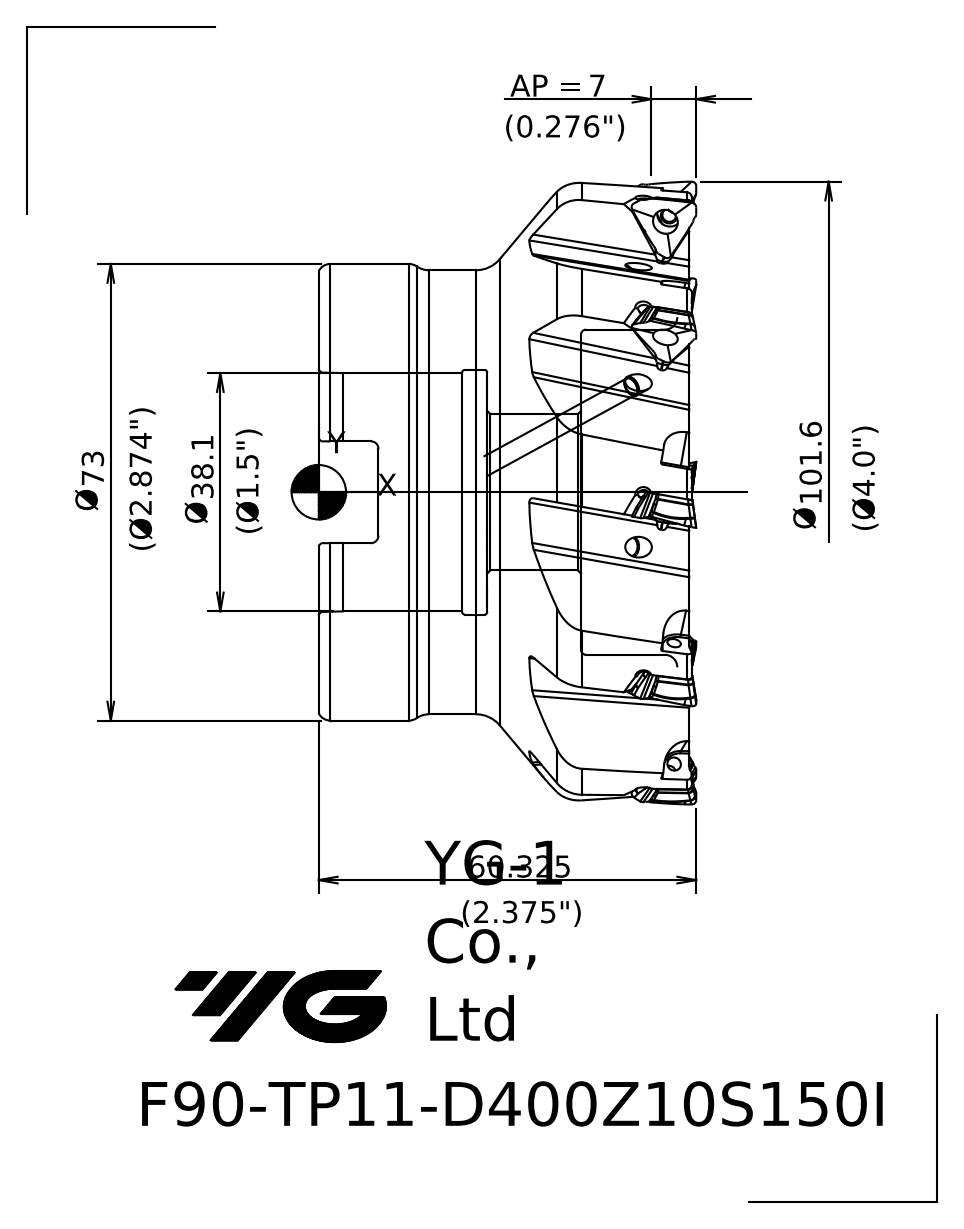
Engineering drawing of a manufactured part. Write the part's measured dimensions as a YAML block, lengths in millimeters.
part_name: "10227F143314p3tx"
step_written_by: "SIEMENS PLM Software NX 10.0 (AP203_CONFIGURATION_CONTROLLED_3D_DESIGN_OF_MECHANICAL_PARTS_AND_ASSEMBLIES_MIM_LF)"
units: millimeters
bodies: {solids: 1, faces: 76, planar: 18, cylindrical: 10, other: 48}
overall_size: [101.65, 101.65, 60.33]
volume: 251620
surface_area: 44282
round_holes:
  - {diameter: 25, count: 1}
  - {diameter: 38.1, count: 1}
  - {diameter: 39.1, count: 1}
  - {diameter: 52, count: 1}
round_bosses_or_shafts:
  - {diameter: 73, count: 1}
  - {diameter: 71, count: 1}
partial_cylinders:
  - {radius: 1.2, count: 2}
face_to_face_distances: [59.23, 17.3, 41.93, 32.3, 15, 26.93, 49.7, 32.4, 17.4, 9.53]
